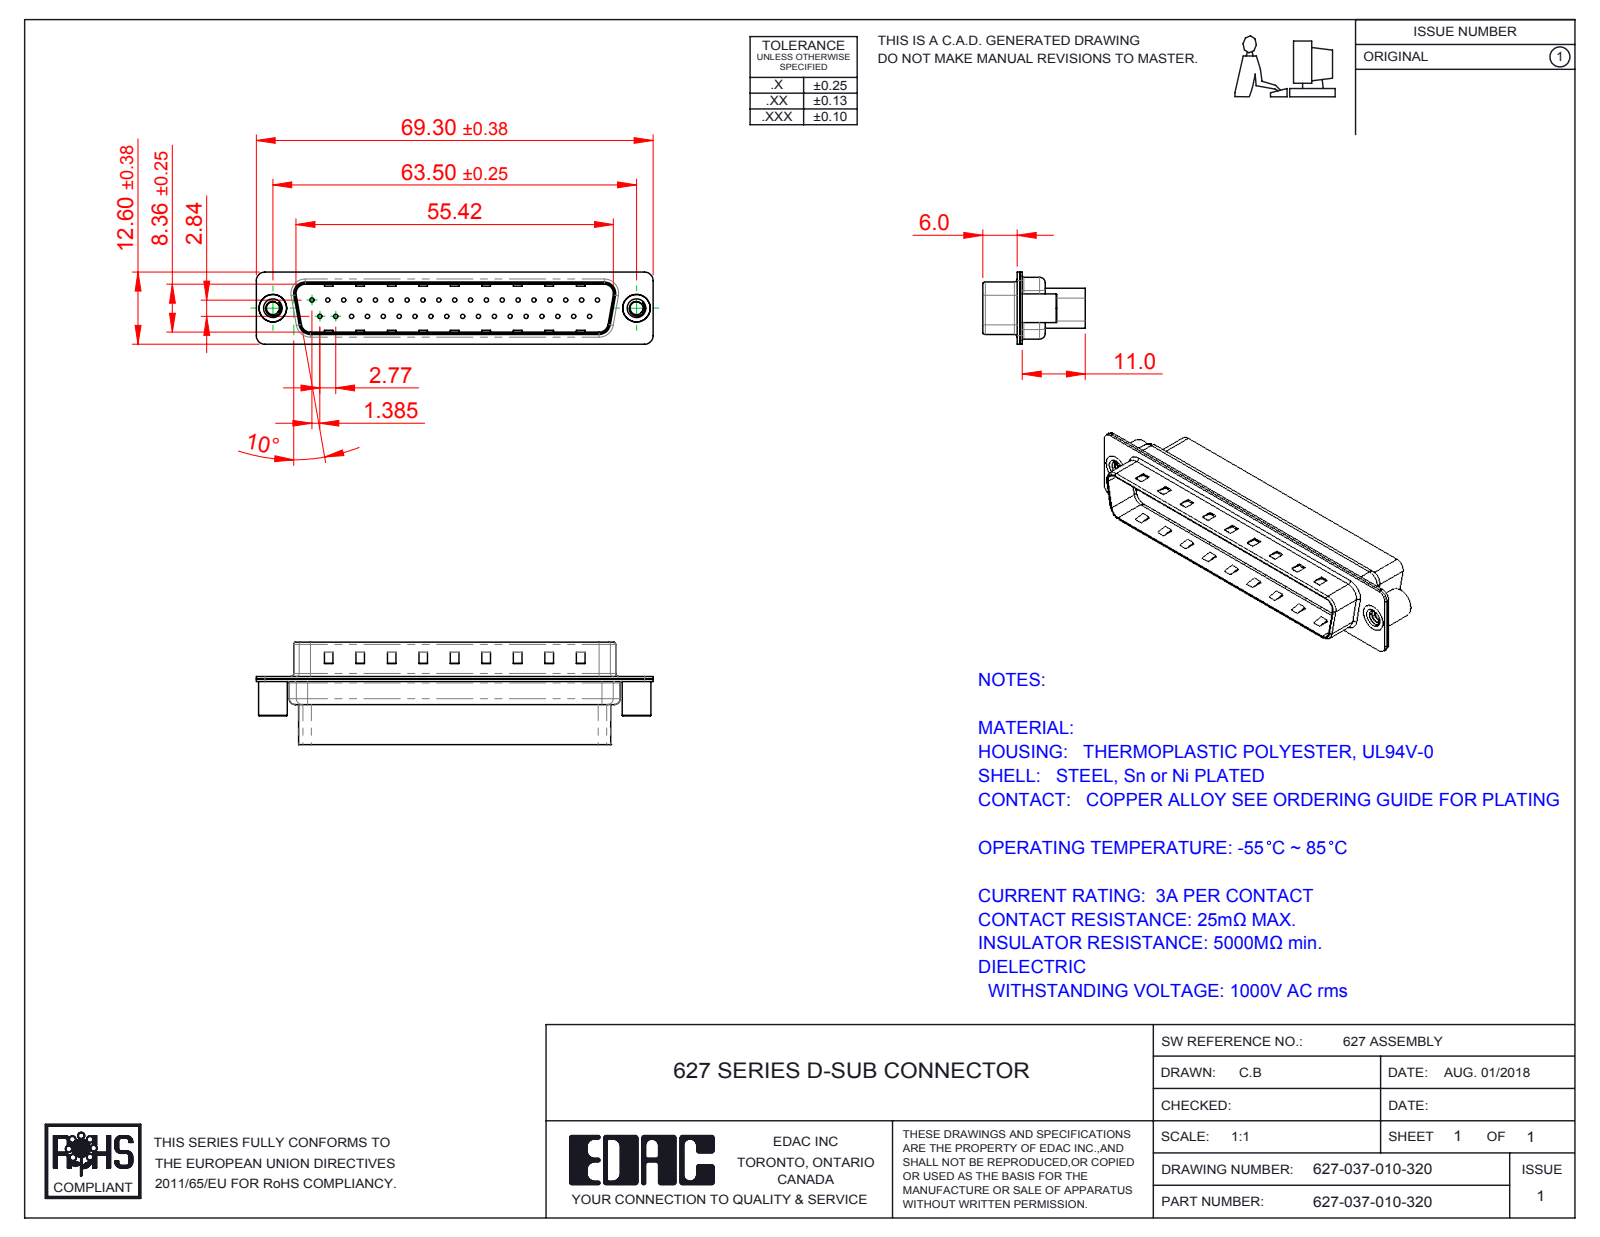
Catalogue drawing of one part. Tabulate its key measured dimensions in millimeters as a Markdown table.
| quantity | value |
| --- | --- |
| part name | 627 Shell Rear_37 Contacts; 627 Shell Front_37 Contacts; 627-050-010-320; 627 4-40 Threaded Standoff BS (+1 more) |
| STEP written by | SolidWorks 2016 (CONFIG_CONTROL_DESIGN) |
| units | millimeters |
| bodies | 5 solids, 730 faces (277 planar, 383 cylindrical, 70 other) |
| overall size | 69.3 × 17.9 × 12.6 |
| volume | 5 120 mm³ |
| surface area | 9 227 mm² |
| round holes (diameter × count) | 0.75 × 37, 1.6 × 37, 2 × 37, 2.26 × 2, 4 × 2, 4.8 × 2 |
| round bosses / shafts (diameter × count) | 5 × 2, 4.9 × 2 |
| partial cylindrical surfaces (radius × count) | 1.5 × 16, 2 × 12, 0.5 × 8, 1.6 × 8, 0.25 × 4, 0.6 × 4, 0.65 × 4, 0.9 × 4 |
| main face-to-face distances | 0.4, 0.82, 9.58, 0.68, 7.68, 0.45, 1.08, 8.08, 8.76, 7 |
| hole center spacings | 3.16, 2.77, 5.54, 8.31, 5.04, 10.1, 11.08, 12.78 |
